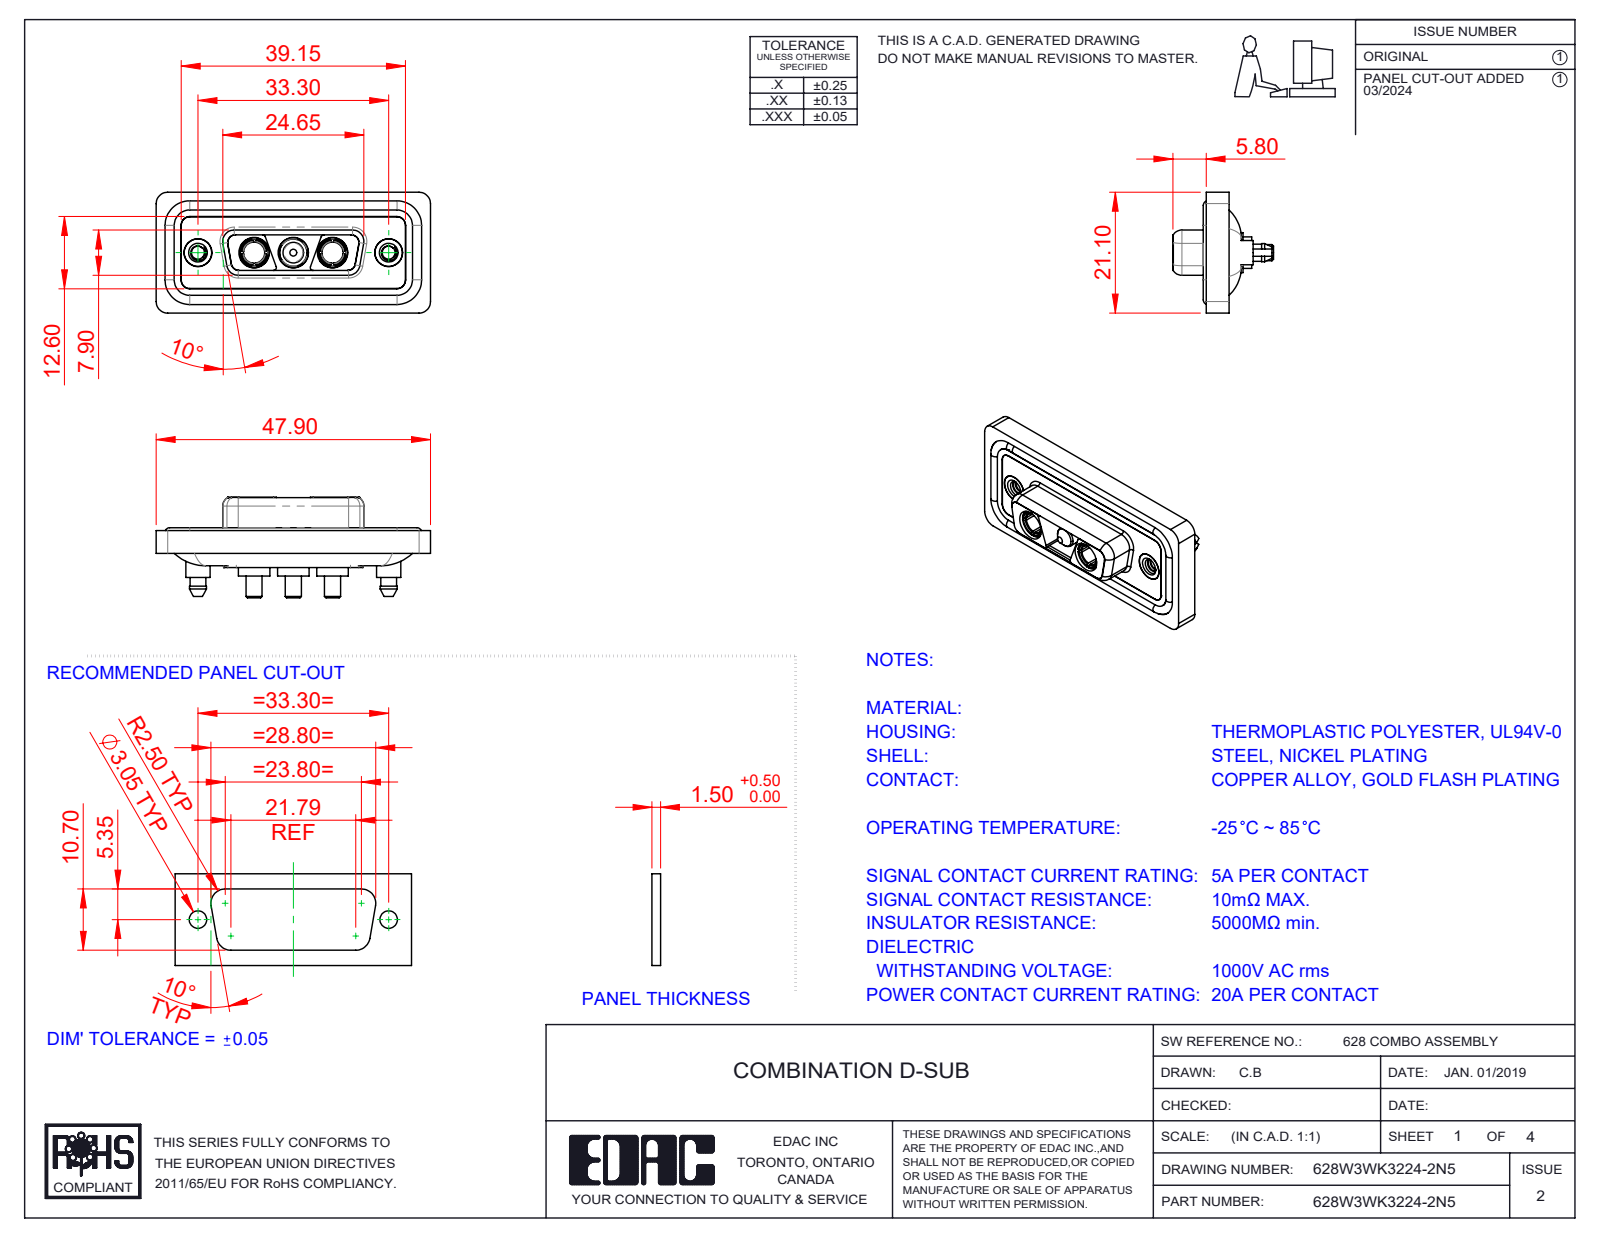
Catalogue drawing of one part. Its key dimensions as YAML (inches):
part_name: "Power Pin_20A S; 628Combo Shell Front_15 Contacts; Power Socket_20A S; 628Combo Housing_3WK3 (+4 more)"
step_written_by: "SolidWorks 2023 (CONFIG_CONTROL_DESIGN)"
units: inches
bodies: {solids: 13, faces: 633, planar: 194, cylindrical: 290, other: 149}
overall_size: [1.886, 0.831, 0.691]
volume: 0.367
surface_area: 15.25
round_holes:
  - {diameter: 0.191, count: 5}
  - {diameter: 0.209, count: 3}
  - {diameter: 0.089, count: 2}
  - {diameter: 0.146, count: 2}
  - {diameter: 0.157, count: 2}
  - {diameter: 0.159, count: 2}
  - {diameter: 0.197, count: 2}
round_bosses_or_shafts:
  - {diameter: 0.063, count: 4}
  - {diameter: 0.217, count: 3}
  - {diameter: 0.205, count: 3}
  - {diameter: 0.187, count: 3}
  - {diameter: 0.148, count: 3}
  - {diameter: 0.11, count: 3}
  - {diameter: 0.213, count: 2}
  - {diameter: 0.195, count: 2}
partial_cylinders:
  - {radius: 0.059, count: 24}
  - {radius: 0.079, count: 20}
  - {radius: 0.053, count: 12}
  - {radius: 0.063, count: 10}
  - {radius: 0.02, count: 8}
  - {radius: 0.01, count: 4}
  - {radius: 0.024, count: 4}
  - {radius: 0.026, count: 4}
face_to_face_distances: [0.016, 0.063, 0.071, 0.02, 0.043, 0.114, 0.222, 0.278, 0.059, 0.211]
hole_center_spacings: [0.27, 0.386, 0.656, 0.925, 0.539, 1.311]
